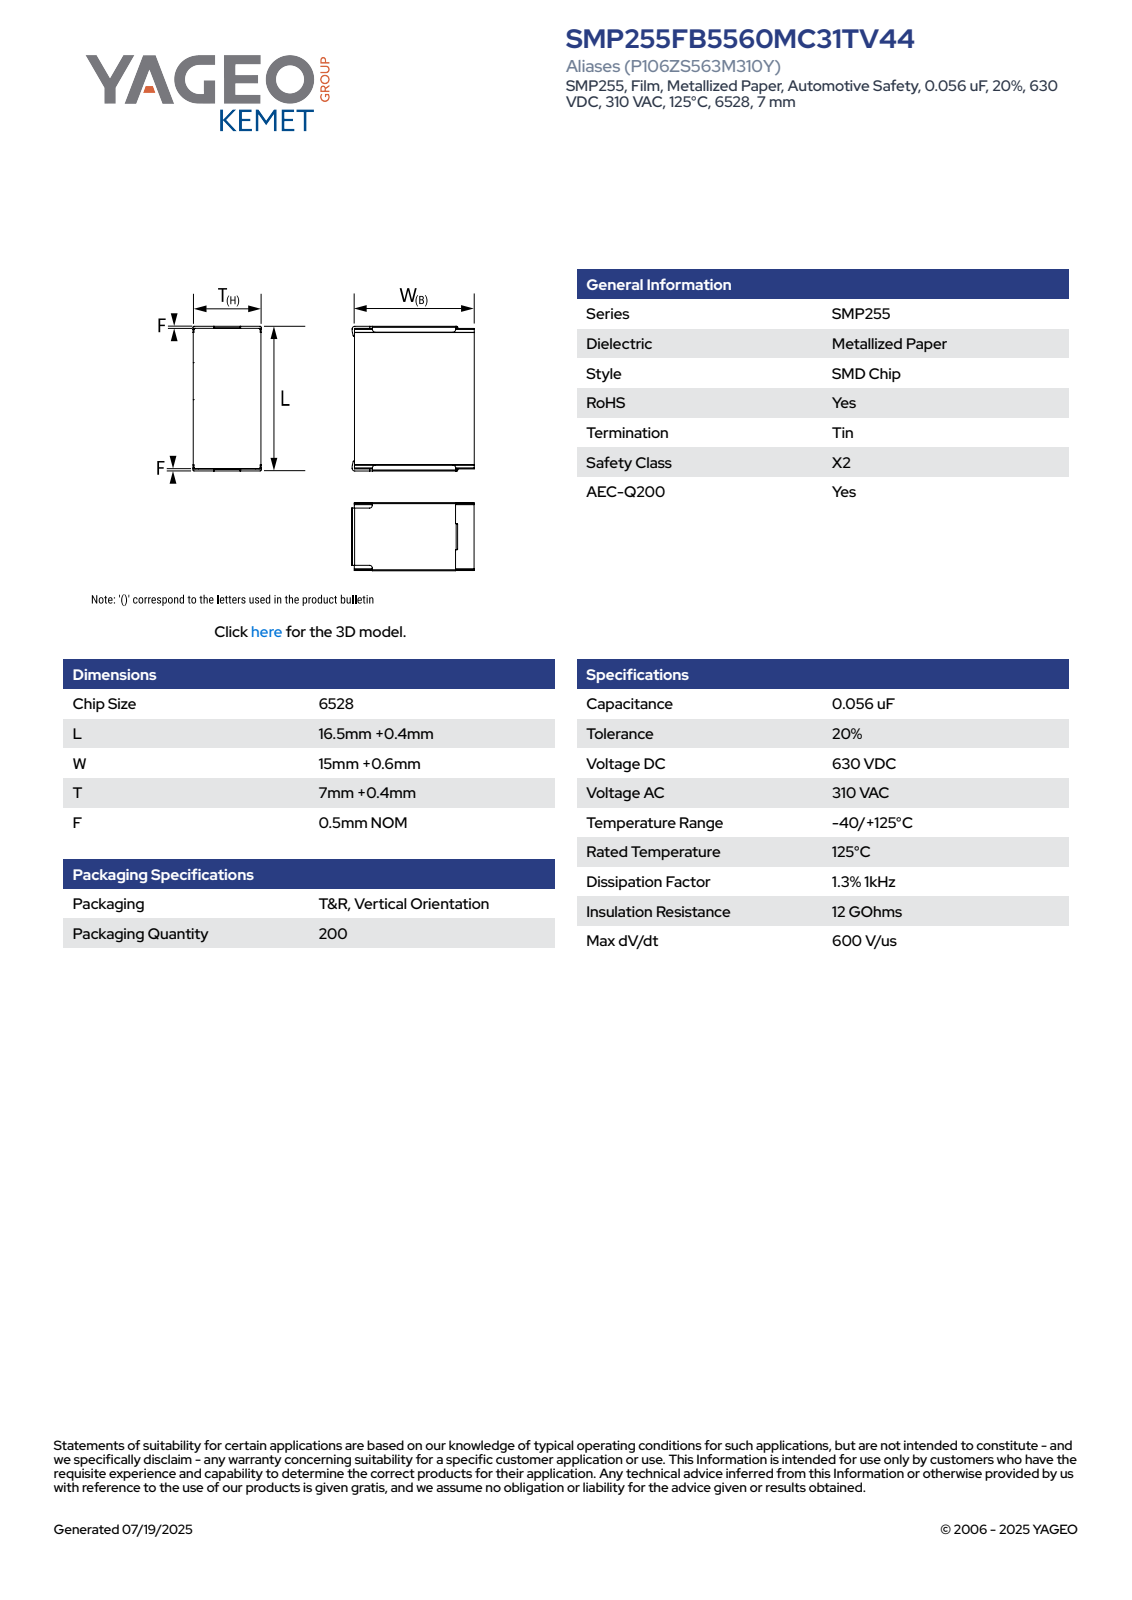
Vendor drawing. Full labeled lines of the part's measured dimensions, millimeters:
Part name (STEP PRODUCT): CFS_KSTD_6528_L16.9W15.6T7.4F0.5
STEP written by: SolidWorks 2021 (AUTOMOTIVE_DESIGN)
Units: millimetres
Bodies: 4 solids, 117 faces (103 planar, 14 cylindrical, 0 other)
Overall size (bounding box): 16.9 × 16.12 × 7.78
Volume: 1 900 mm³ · Surface area: 1 071 mm²
Partial cylindrical surfaces — rounded edges, fillets, slot ends (radius × count): R0.44 ×10, R0.59 ×4
Main face-to-face distances: 7.4, 16.9, 14.98, 0.5, 16.4, 7.59, 0.62, 15.9, 7.78, 15.6
